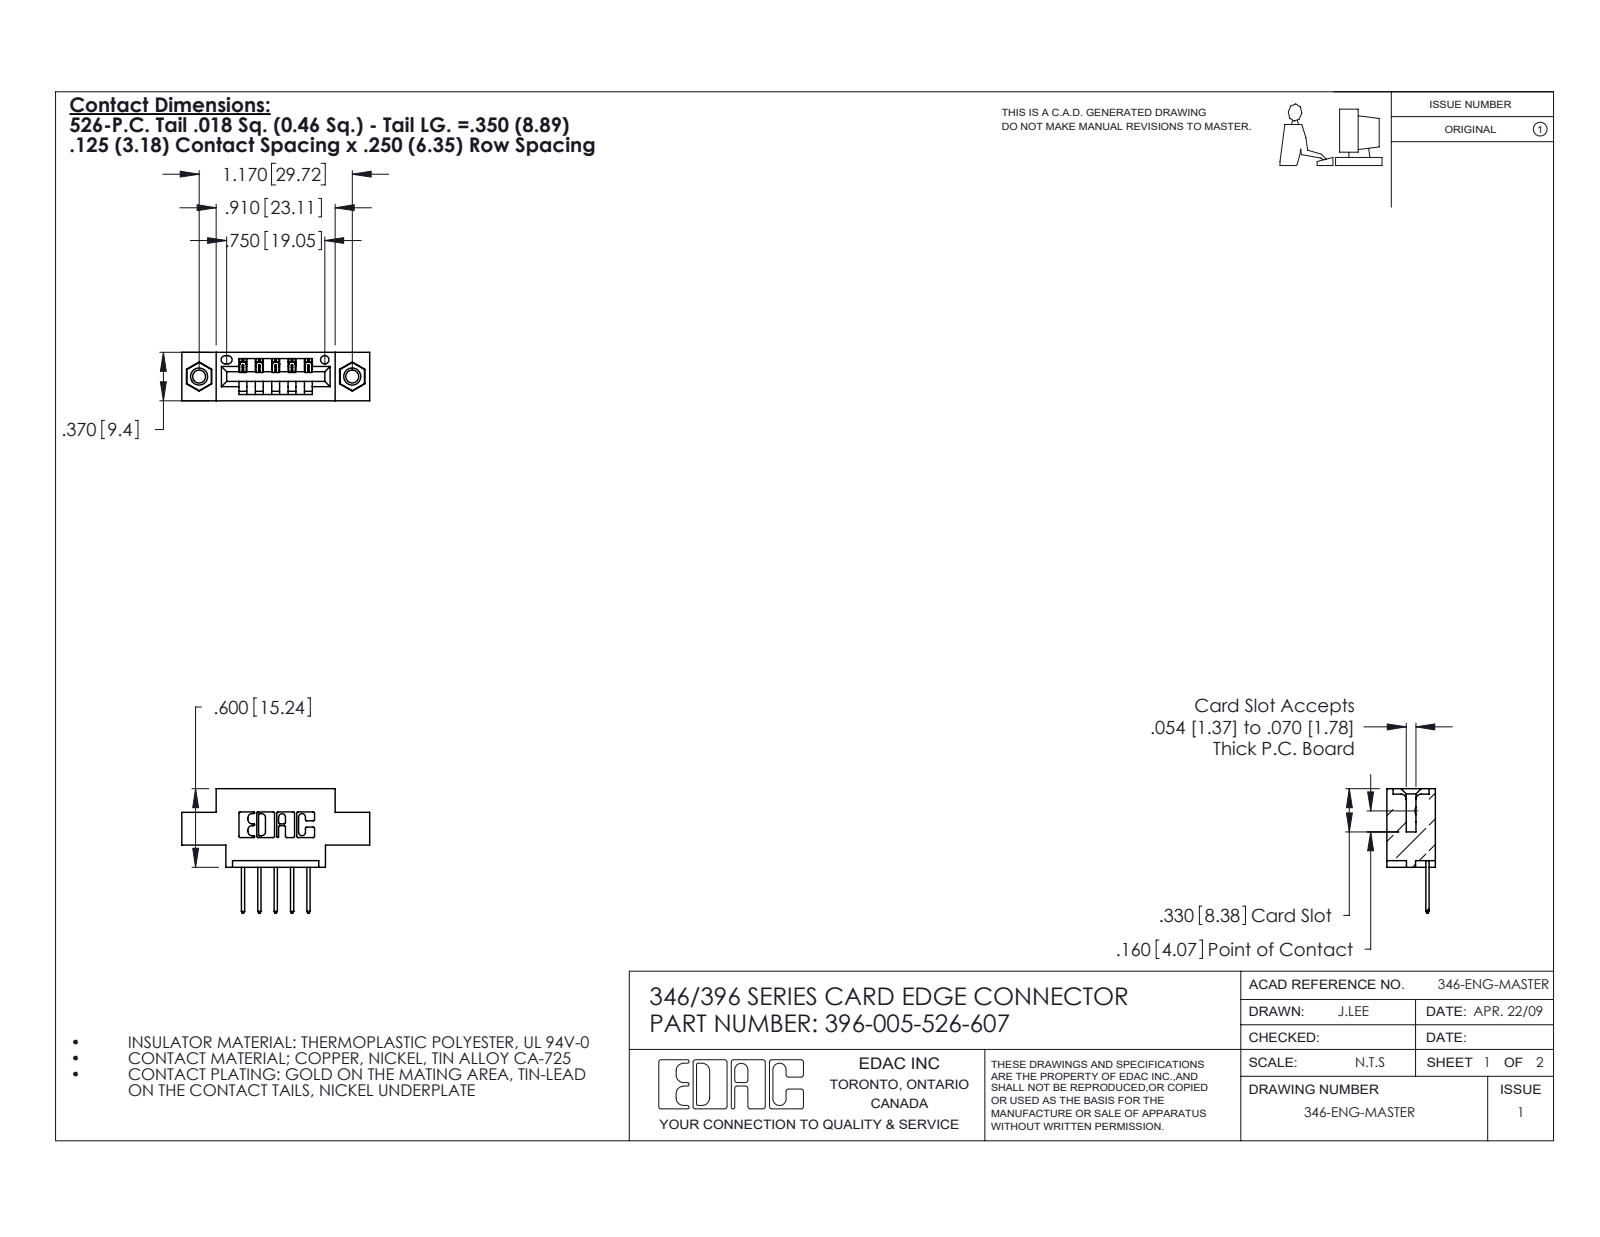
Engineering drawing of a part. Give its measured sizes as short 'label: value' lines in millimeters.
name: 396-005-526-607; 346 Part_0.170 Offset - 0.156 Dia-TI; 345-250-001_345-250-005-103; 345-292-001_345-293-126
written by: SolidWorks 2020 (CONFIG_CONTROL_DESIGN)
unit: mm
bodies: 8 solids, 476 faces (312 planar, 148 cylindrical, 16 other)
size: 36.4 × 24.1 × 9.4
volume: 3 060 mm³; area: 3 618 mm²
holes: 2× ⌀2.5, 2× ⌀3.2, 2× ⌀4, 1× ⌀1.6
bosses: 2× ⌀3.9
rounds: 22× R0.3, 10× R0.2, 10× R0.3, 6× R0.2, 6× R0.8, 3× R0.7, 2× R0.8, 2× R1
face distances: 6.4, 9.4, 1.2, 8.2, 5.6, 3.8, 2.5, 4.4, 14, 1.8
hole spacings: 6.2, 24.6, 29.7
